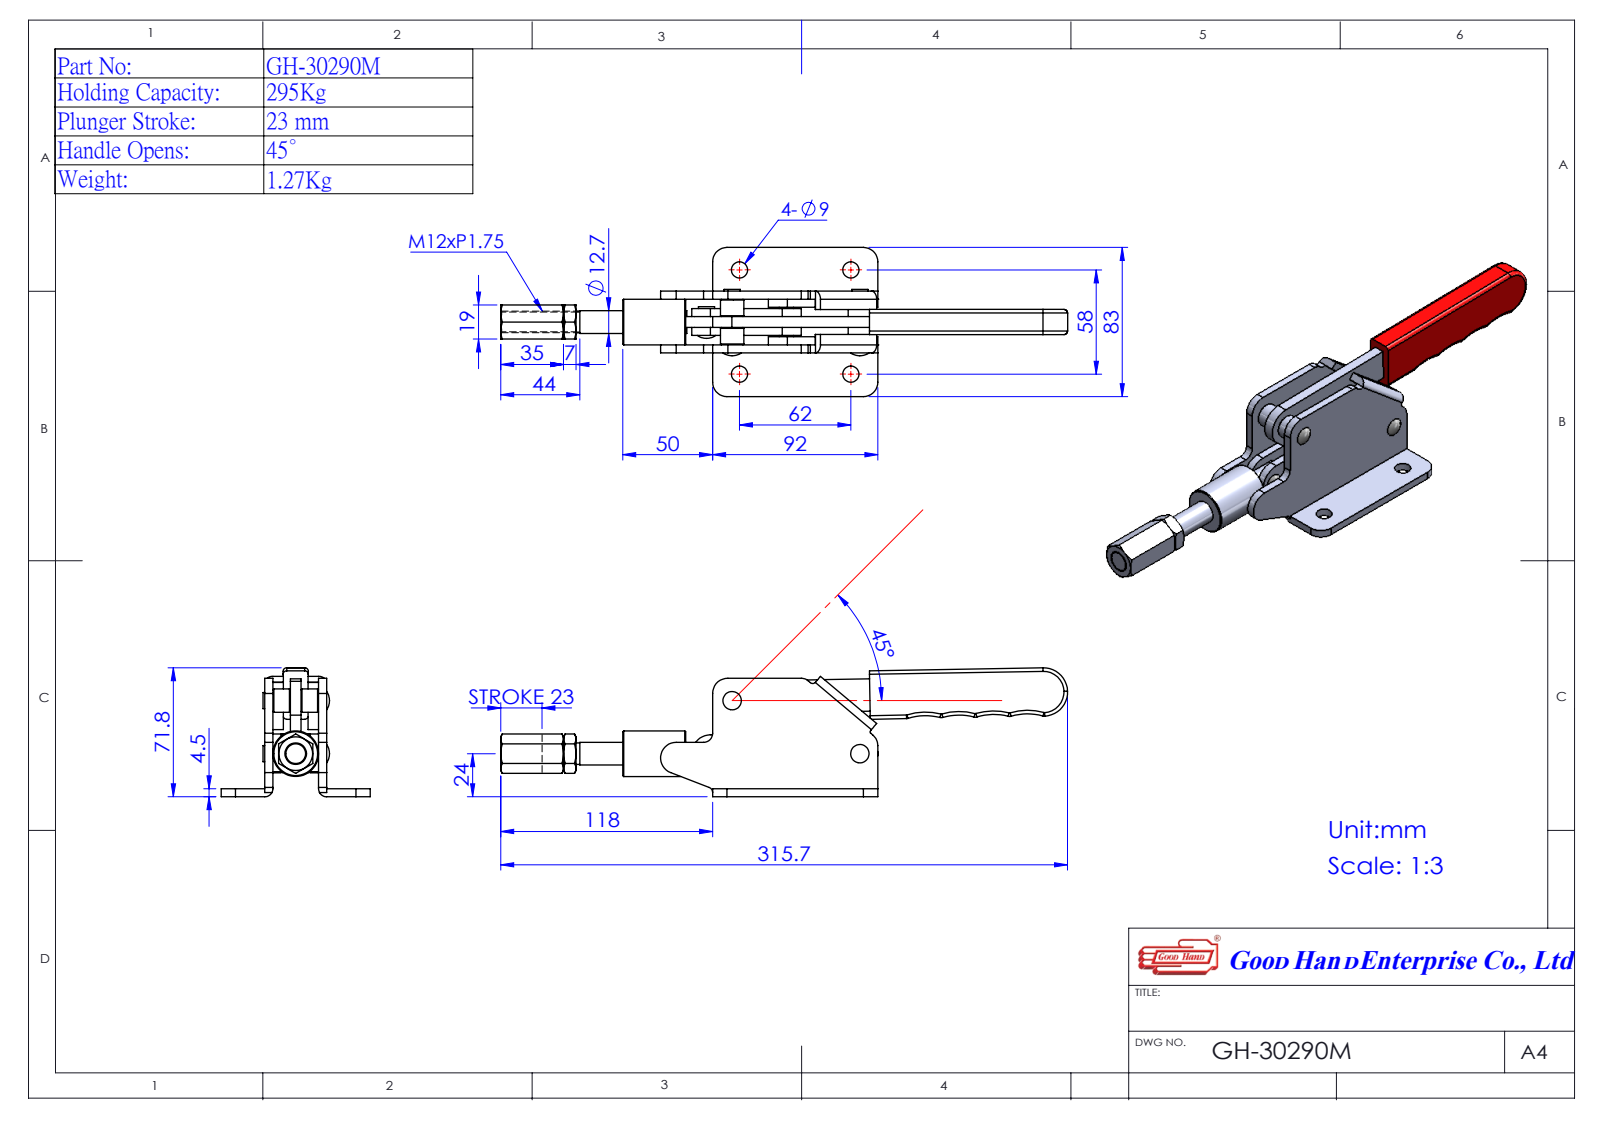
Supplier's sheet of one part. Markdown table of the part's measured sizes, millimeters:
| quantity | value |
| --- | --- |
| part name | GH-30290M(簡化); 430290M33-1^GH-30290M(簡化); Group6^GH-30290M(簡化); Group4^GH-30290M(簡化) (+3 more) |
| STEP written by | SolidWorks 2016 (AUTOMOTIVE_DESIGN) |
| units | millimeters |
| bodies | 9 solids, 226 faces (99 planar, 109 cylindrical, 18 other) |
| overall size | 315.76 × 83 × 68.04 |
| volume | 191 151 mm³ |
| surface area | 82 782 mm² |
| round holes (diameter × count) | 6 × 4, 9 × 4, 12 × 1, 12.7 × 1 |
| round bosses / shafts (diameter × count) | 9 × 3, 25.4 × 1, 13 × 1, 5.67 × 1 |
| partial cylindrical surfaces (radius × count) | 3 × 8, 1 × 4, 8 × 4, 10.5 × 4, 32 × 4, 2 × 1, 5 × 1, 6 × 1 |
| main face-to-face distances | 4.5, 29.9, 9.7, 20.2, 15.7, 25.4, 14.2, 10, 10.2, 24.2 |
| hole center spacings | 58, 62, 84.9, 32.76, 40.9, 42.9, 44.5, 77 |
